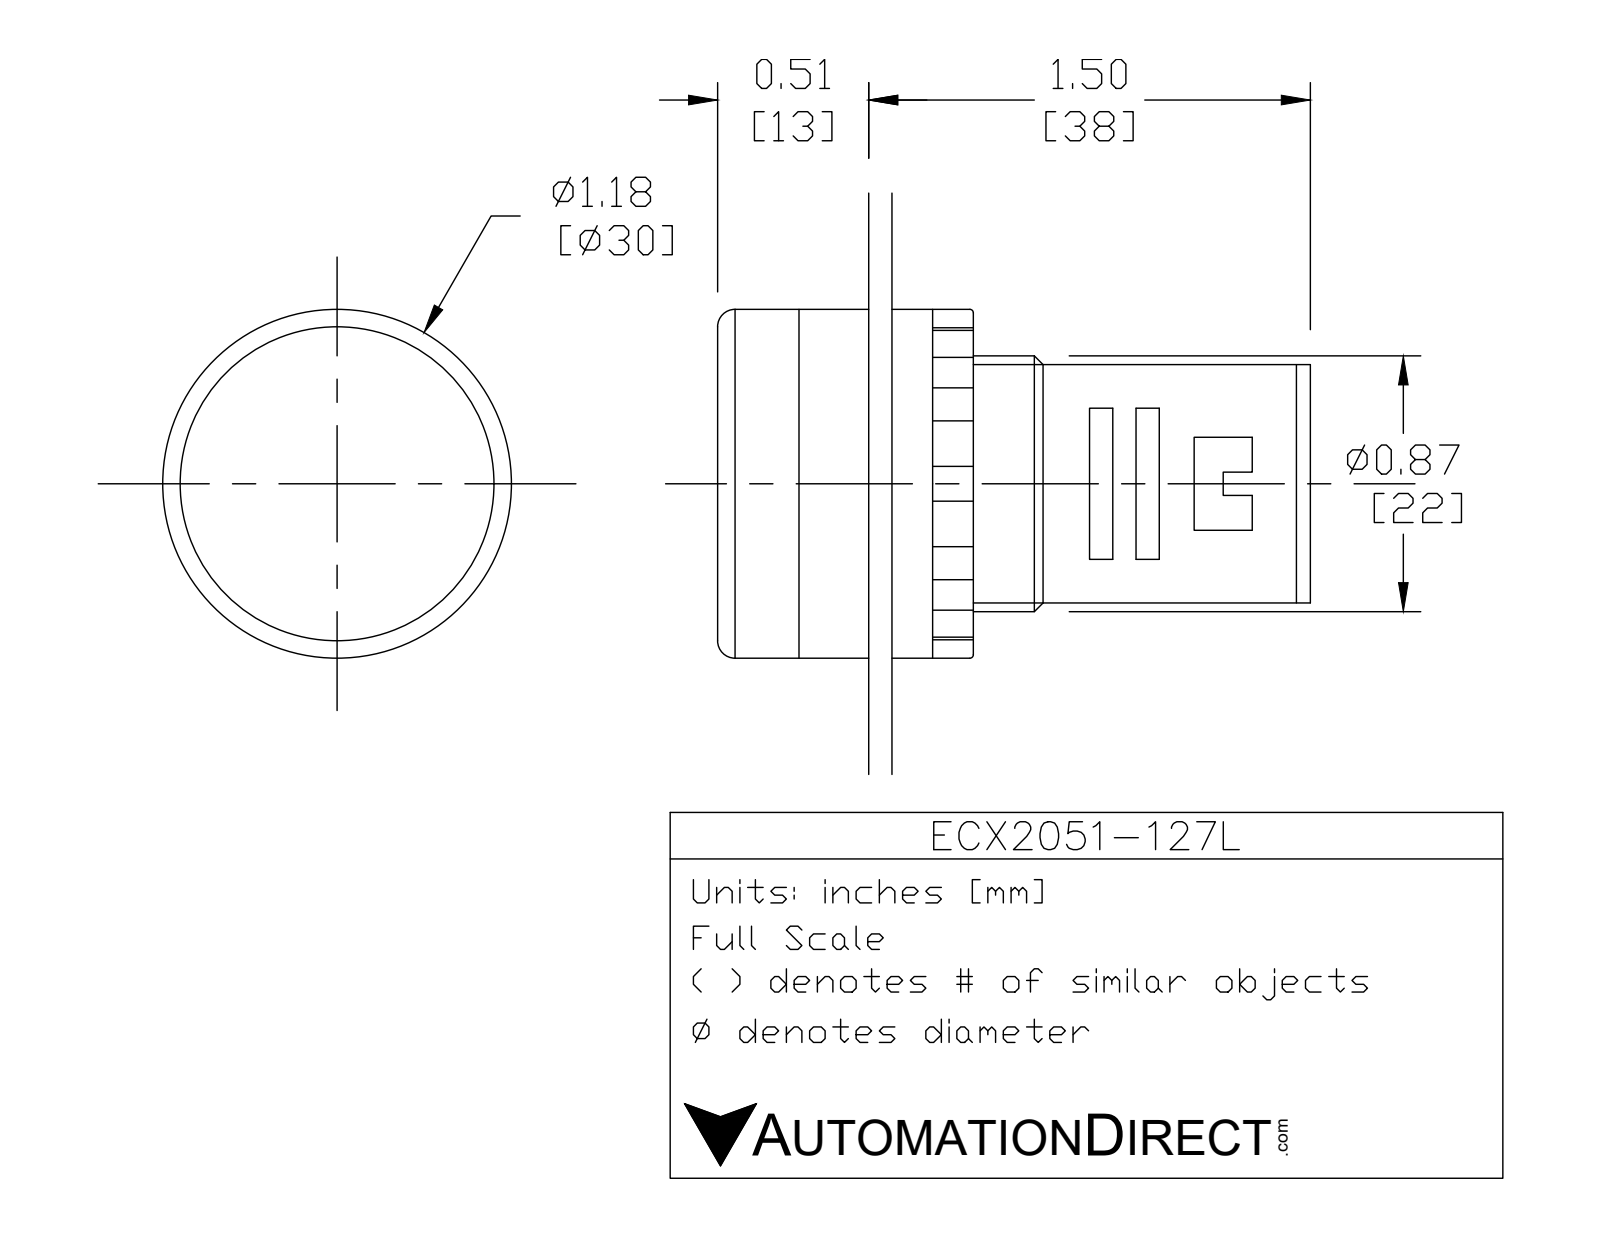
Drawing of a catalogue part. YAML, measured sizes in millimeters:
part_name: "ECX2051-127L"
step_written_by: "SolidWorks 2017 (AUTOMOTIVE_DESIGN)"
units: millimeters
bodies: {solids: 6, faces: 123, planar: 63, cylindrical: 39, other: 21}
overall_size: [51, 30, 30]
volume: 22483
surface_area: 9831
round_holes:
  - {diameter: 5.5, count: 2}
  - {diameter: 22.5, count: 1}
round_bosses_or_shafts:
  - {diameter: 4, count: 2}
  - {diameter: 30, count: 1}
  - {diameter: 29, count: 1}
  - {diameter: 26.5, count: 1}
  - {diameter: 22, count: 1}
  - {diameter: 20, count: 1}
partial_cylinders:
  - {radius: 1, count: 12}
face_to_face_distances: [6, 19, 13, 7, 2, 25, 4, 12, 17, 15]
hole_center_spacings: [4.62, 9.24]
